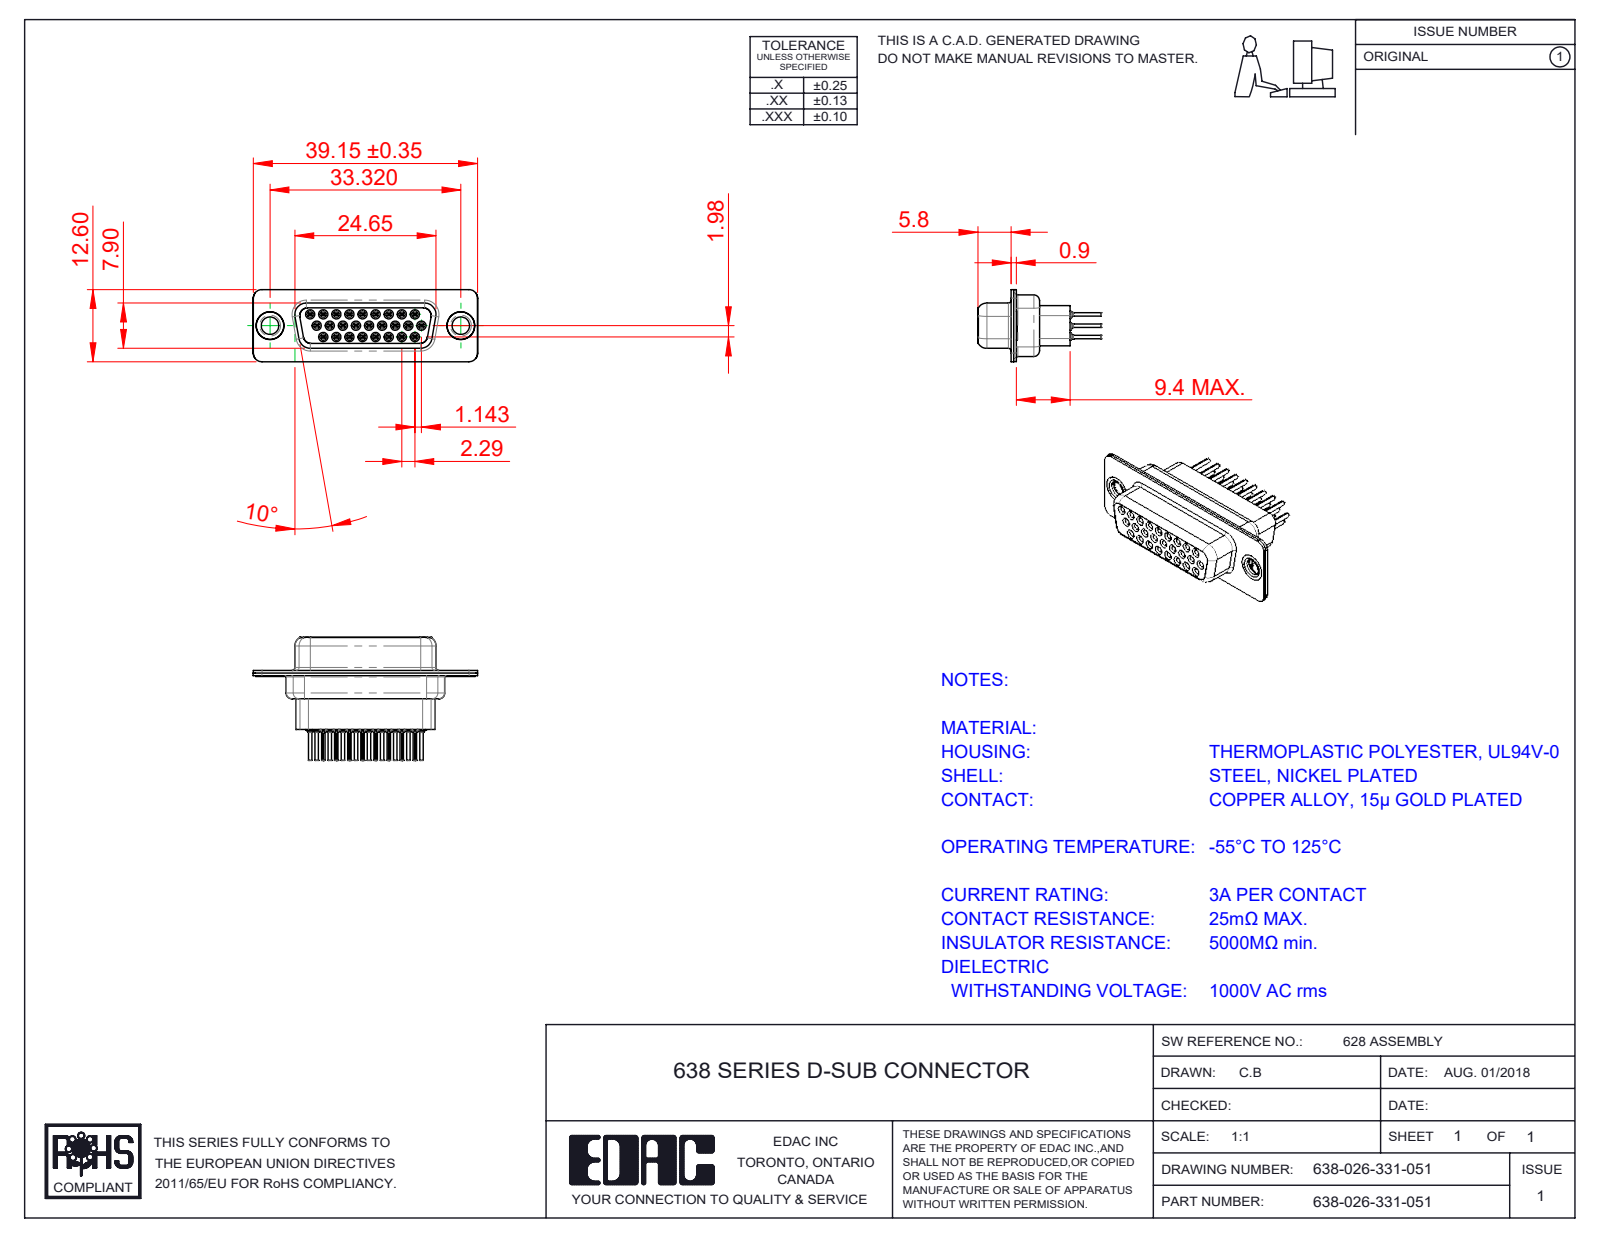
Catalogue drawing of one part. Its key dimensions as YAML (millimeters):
part_name: "638 Thru Hole Rivet; 638 Contact Row 3_31; 638-026-331-051; 638 Contact Row 1_31 (+4 more)"
step_written_by: "SolidWorks 2020 (CONFIG_CONTROL_DESIGN)"
units: millimeters
bodies: {solids: 31, faces: 3451, planar: 873, cylindrical: 979, other: 1599}
overall_size: [39.19, 21.5, 12.6]
volume: 2598
surface_area: 9726
round_holes:
  - {diameter: 0.2, count: 26}
  - {diameter: 0.8, count: 26}
  - {diameter: 1, count: 26}
  - {diameter: 1.1, count: 26}
  - {diameter: 1.6, count: 26}
  - {diameter: 1.7, count: 26}
  - {diameter: 1.8, count: 26}
  - {diameter: 3.05, count: 2}
  - {diameter: 4, count: 2}
  - {diameter: 4.05, count: 2}
  - {diameter: 4.85, count: 2}
round_bosses_or_shafts:
  - {diameter: 2, count: 26}
  - {diameter: 1.5, count: 26}
  - {diameter: 1.2, count: 26}
  - {diameter: 0.6, count: 26}
  - {diameter: 5, count: 2}
  - {diameter: 4.95, count: 2}
  - {diameter: 4.8, count: 2}
  - {diameter: 3.55, count: 2}
partial_cylinders:
  - {radius: 0.1, count: 52}
  - {radius: 1.5, count: 20}
  - {radius: 0.28, count: 18}
  - {radius: 2, count: 12}
  - {radius: 1.55, count: 8}
  - {radius: 1.35, count: 5}
  - {radius: 0.25, count: 4}
  - {radius: 0.5, count: 4}
face_to_face_distances: [0.45, 0.4, 6.6, 1.43, 8.88, 0.9, 7, 2.28, 6.2, 5.8]
hole_center_spacings: [3.96, 2.28, 4.57, 6.05, 2.29, 8.24, 6.86, 10.48]
